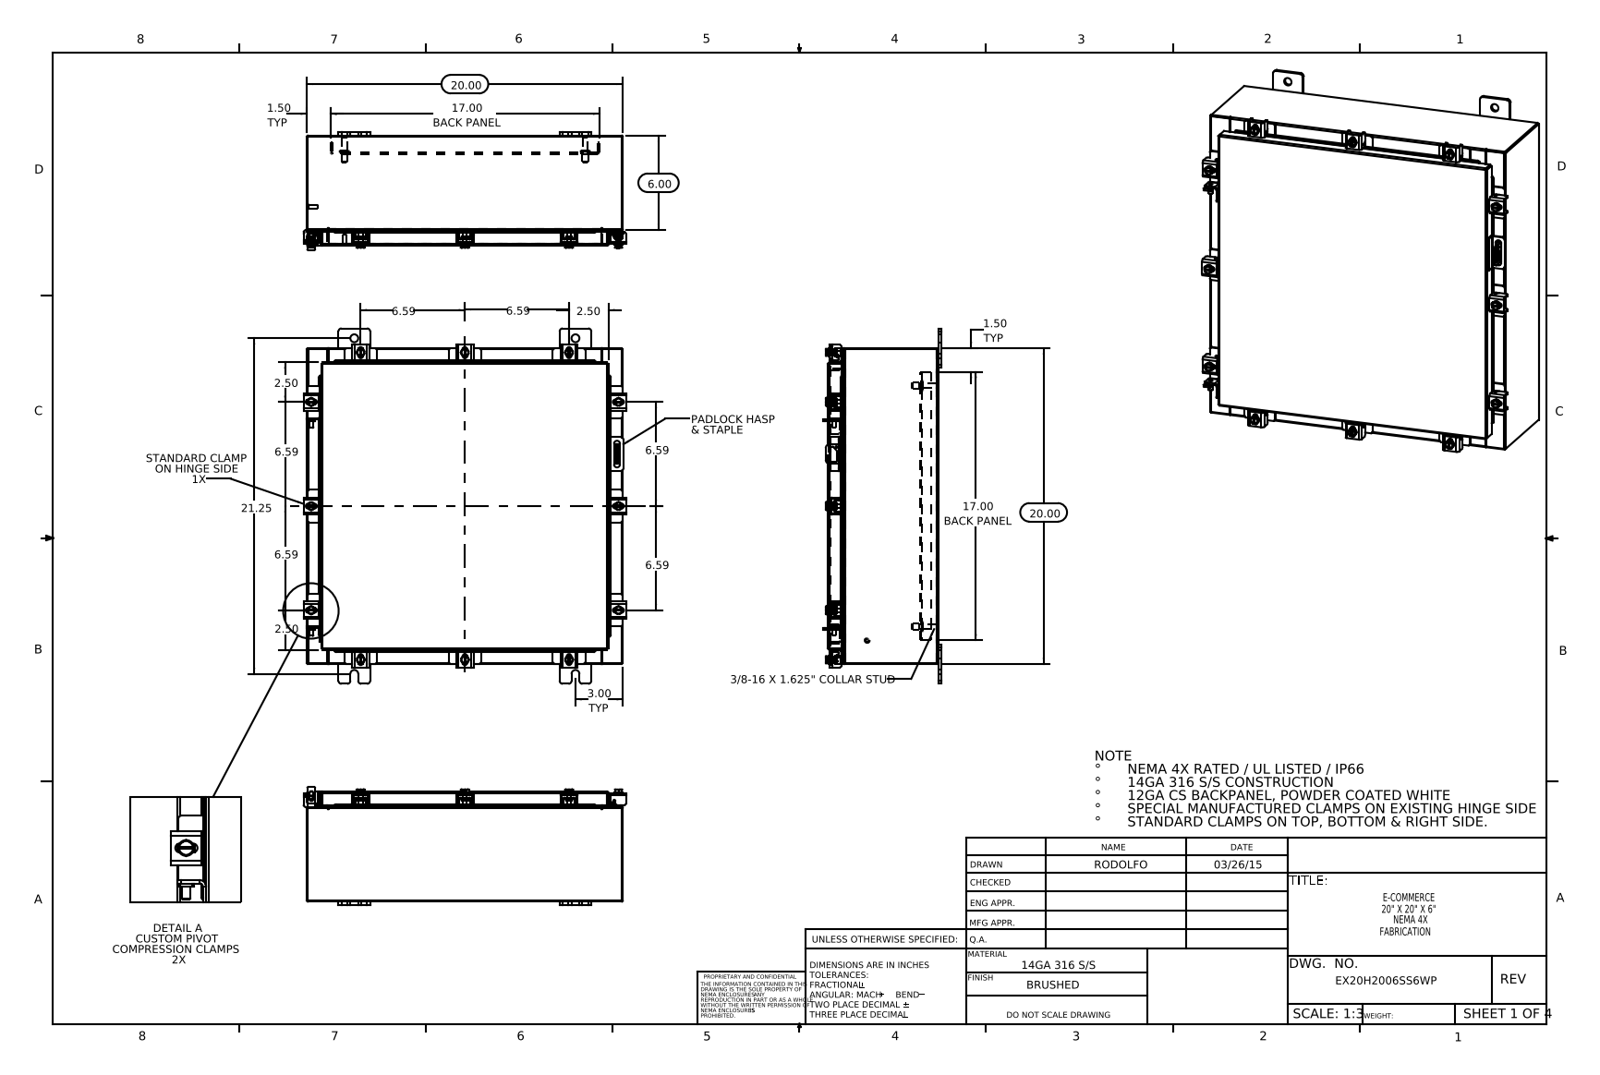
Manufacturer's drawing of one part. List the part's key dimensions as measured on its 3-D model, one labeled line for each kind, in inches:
Part name (STEP PRODUCT): 22104005_DEFAULT_RTP30; EX20H2006SS6WP Bottom; EX20H2006SS6WP Padlock Hasp; Special Clamp Assembly (+8 more)
STEP written by: SolidWorks 2014 (CONFIG_CONTROL_DESIGN)
Units: inches
Bodies: 81 solids, 2018 faces (1075 planar, 783 cylindrical, 160 other)
Overall size (bounding box): 22.5 × 20.421 × 7.453
Volume: 149.7 in³ · Surface area: 3 735 in²
Round holes (diameter × count): ⌀0.213 ×12, ⌀0.26 ×12, ⌀0.5 ×8, ⌀0.125 ×1, ⌀0.25 ×1
Round bosses / shafts (diameter × count): ⌀0.5 ×12, ⌀0.25 ×12, ⌀0.399 ×10, ⌀0.625 ×4, ⌀0.375 ×4, ⌀0.33 ×4, ⌀0.315 ×2, ⌀0.236 ×2
Partial cylindrical surfaces — rounded edges, fillets, slot ends (radius × count): R0.06 ×54, R0.013 ×24, R0.141 ×24, R0.19 ×24, R0.088 ×22, R0.12 ×22, R0.09 ×18, R0.05 ×17
Main face-to-face distances: 0.075, 6.9, 19.925, 6.975, 6.826, 0.104, 1, 1.075, 5.826, 5.9
Hole centre spacings: 6.594, 10.217, 16.617, 18.998, 20.539, 2.34, 14.374, 17.381
